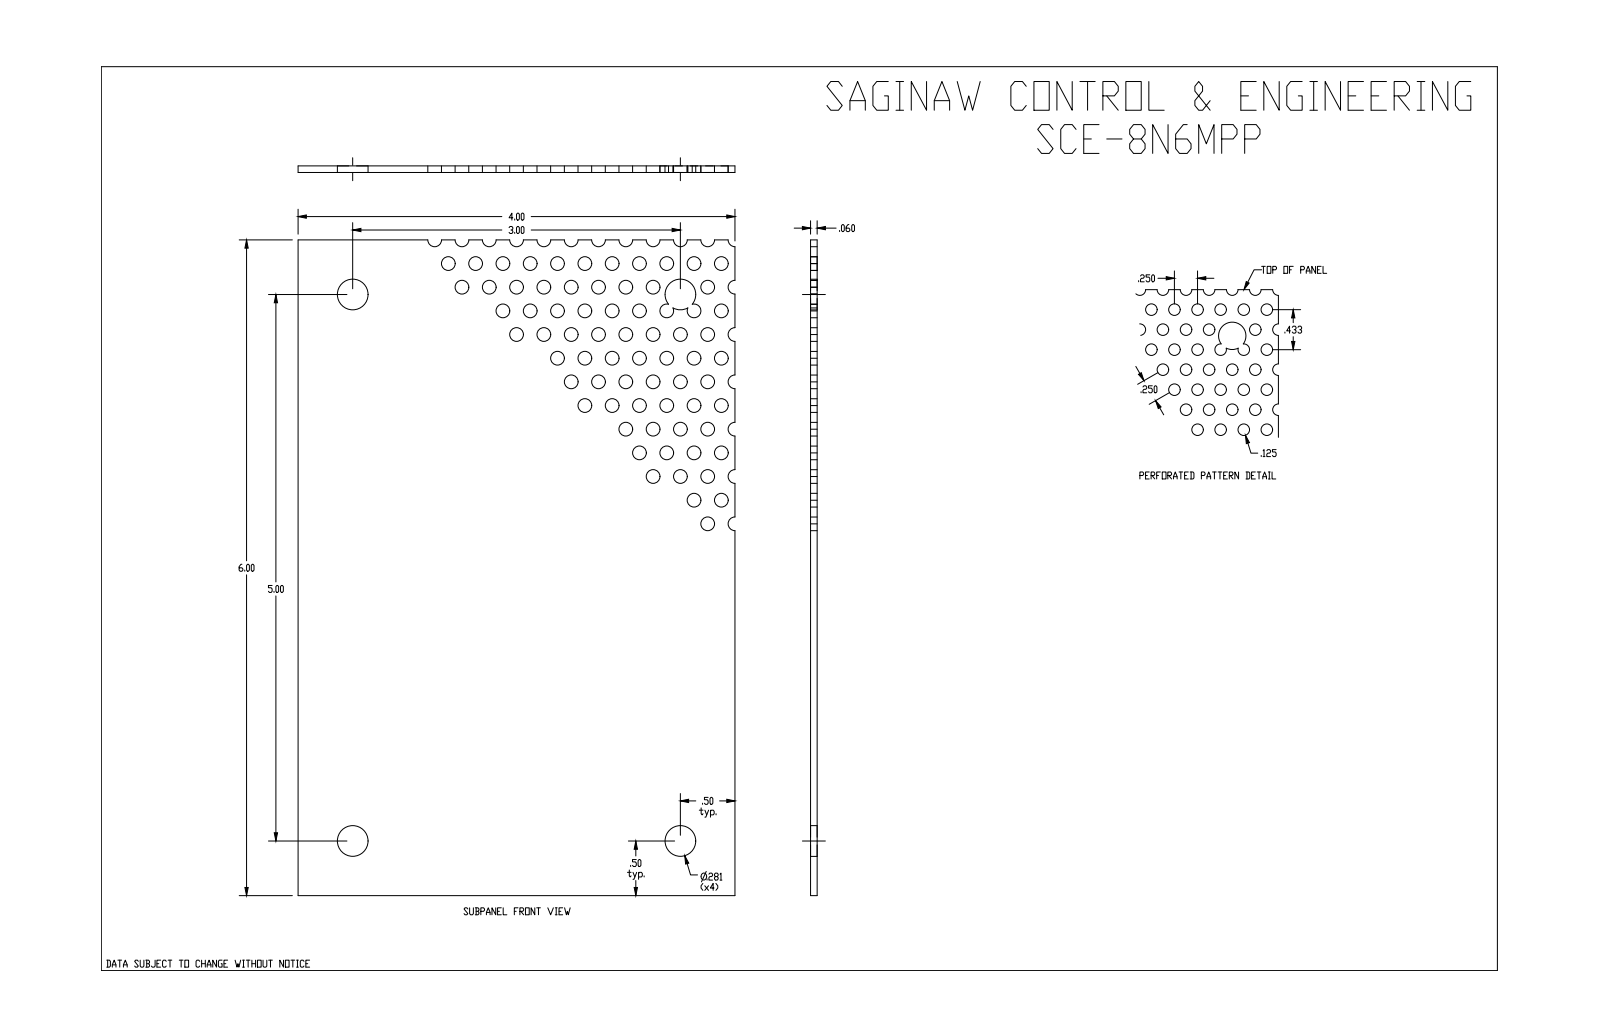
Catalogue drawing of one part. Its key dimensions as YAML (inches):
part_name: "SCE-8N6MPP"
step_written_by: "SolidWorks 2019 (CONFIG_CONTROL_DESIGN)"
units: inches
bodies: {solids: 1, faces: 116, planar: 23, cylindrical: 93, other: 0}
overall_size: [6, 4, 0.06]
volume: 1.367
surface_area: 48.69
round_holes:
  - {diameter: 0.125, count: 58}
  - {diameter: 0.125, count: 12}
  - {diameter: 0.281, count: 4}
partial_cylinders:
  - {radius: 0.062, count: 14}
  - {radius: 0.063, count: 4}
face_to_face_distances: [0.06, 4, 6]
hole_center_spacings: [0.25, 0.5, 0.661, 0.433, 0.433, 0.901, 0.75, 1.323]
